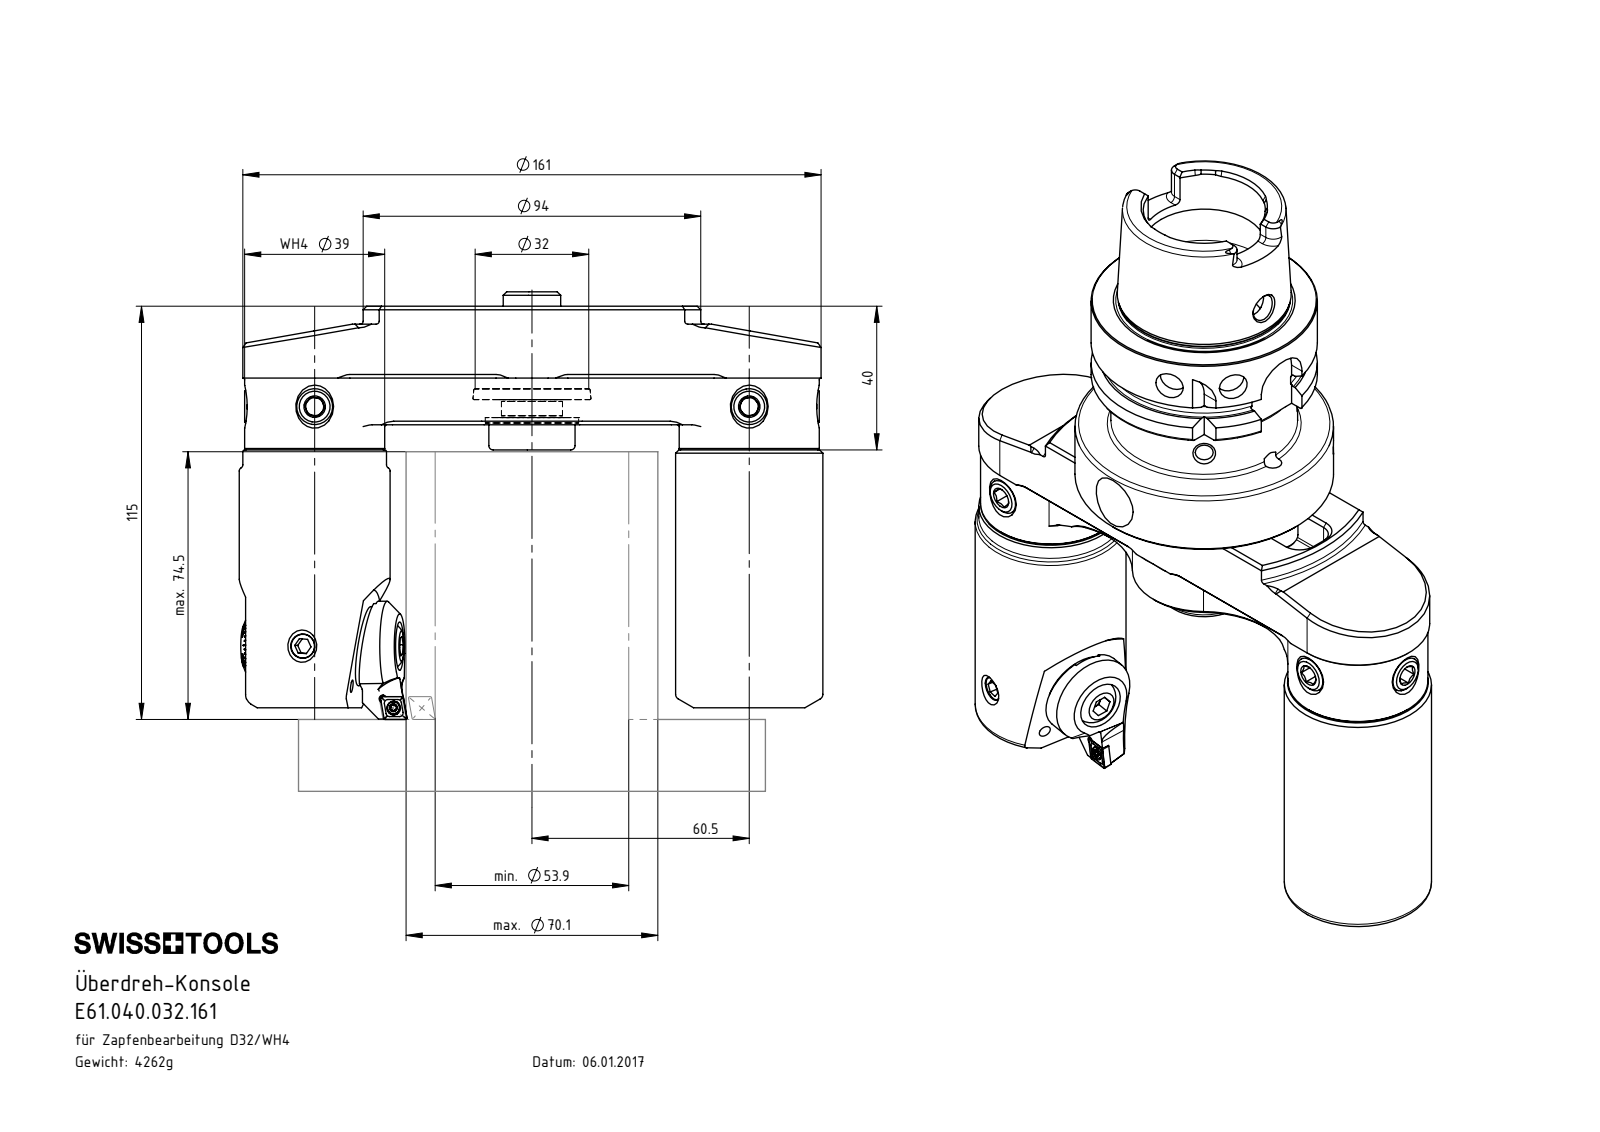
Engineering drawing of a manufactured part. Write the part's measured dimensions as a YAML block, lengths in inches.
part_name: "D32-ER2.001.022_B; Klebstoff D8; WCA-ER2.001.006_A; HA6-D32.K01.060_E_Fertigbearbeitung (+8 more)"
step_written_by: "SolidWorks 2017 (CONFIG_CONTROL_DESIGN)"
units: inches
bodies: {solids: 28, faces: 1179, planar: 535, cylindrical: 221, other: 423}
overall_size: [8.146, 6.398, 2.835]
volume: 32.57
surface_area: 201
round_holes:
  - {diameter: 0.197, count: 9}
  - {diameter: 0.165, count: 6}
  - {diameter: 0.13, count: 4}
  - {diameter: 0.268, count: 4}
  - {diameter: 0.236, count: 3}
  - {diameter: 0.315, count: 3}
  - {diameter: 0.354, count: 3}
  - {diameter: 0.866, count: 3}
  - {diameter: 0.098, count: 2}
  - {diameter: 0.472, count: 2}
  - {diameter: 0.551, count: 2}
  - {diameter: 0.906, count: 2}
round_bosses_or_shafts:
  - {diameter: 0.394, count: 3}
  - {diameter: 1.575, count: 2}
  - {diameter: 1.535, count: 2}
  - {diameter: 0.839, count: 2}
  - {diameter: 0.551, count: 2}
  - {diameter: 0.512, count: 2}
  - {diameter: 0.315, count: 2}
  - {diameter: 0.236, count: 2}
partial_cylinders:
  - {radius: 0.008, count: 12}
  - {radius: 0.014, count: 9}
  - {radius: 0.02, count: 8}
  - {radius: 0.055, count: 6}
  - {radius: 0.113, count: 4}
  - {radius: 0.157, count: 4}
  - {radius: 0.177, count: 4}
  - {radius: 0.315, count: 4}
face_to_face_distances: [1.575, 0.276, 0.787, 0.512, 0.551, 0.079, 0.63, 0.709, 0.197, 1.102]
hole_center_spacings: [0.482, 0.632, 0.682, 0.798, 1.445, 2.069, 2.744, 0.964]
